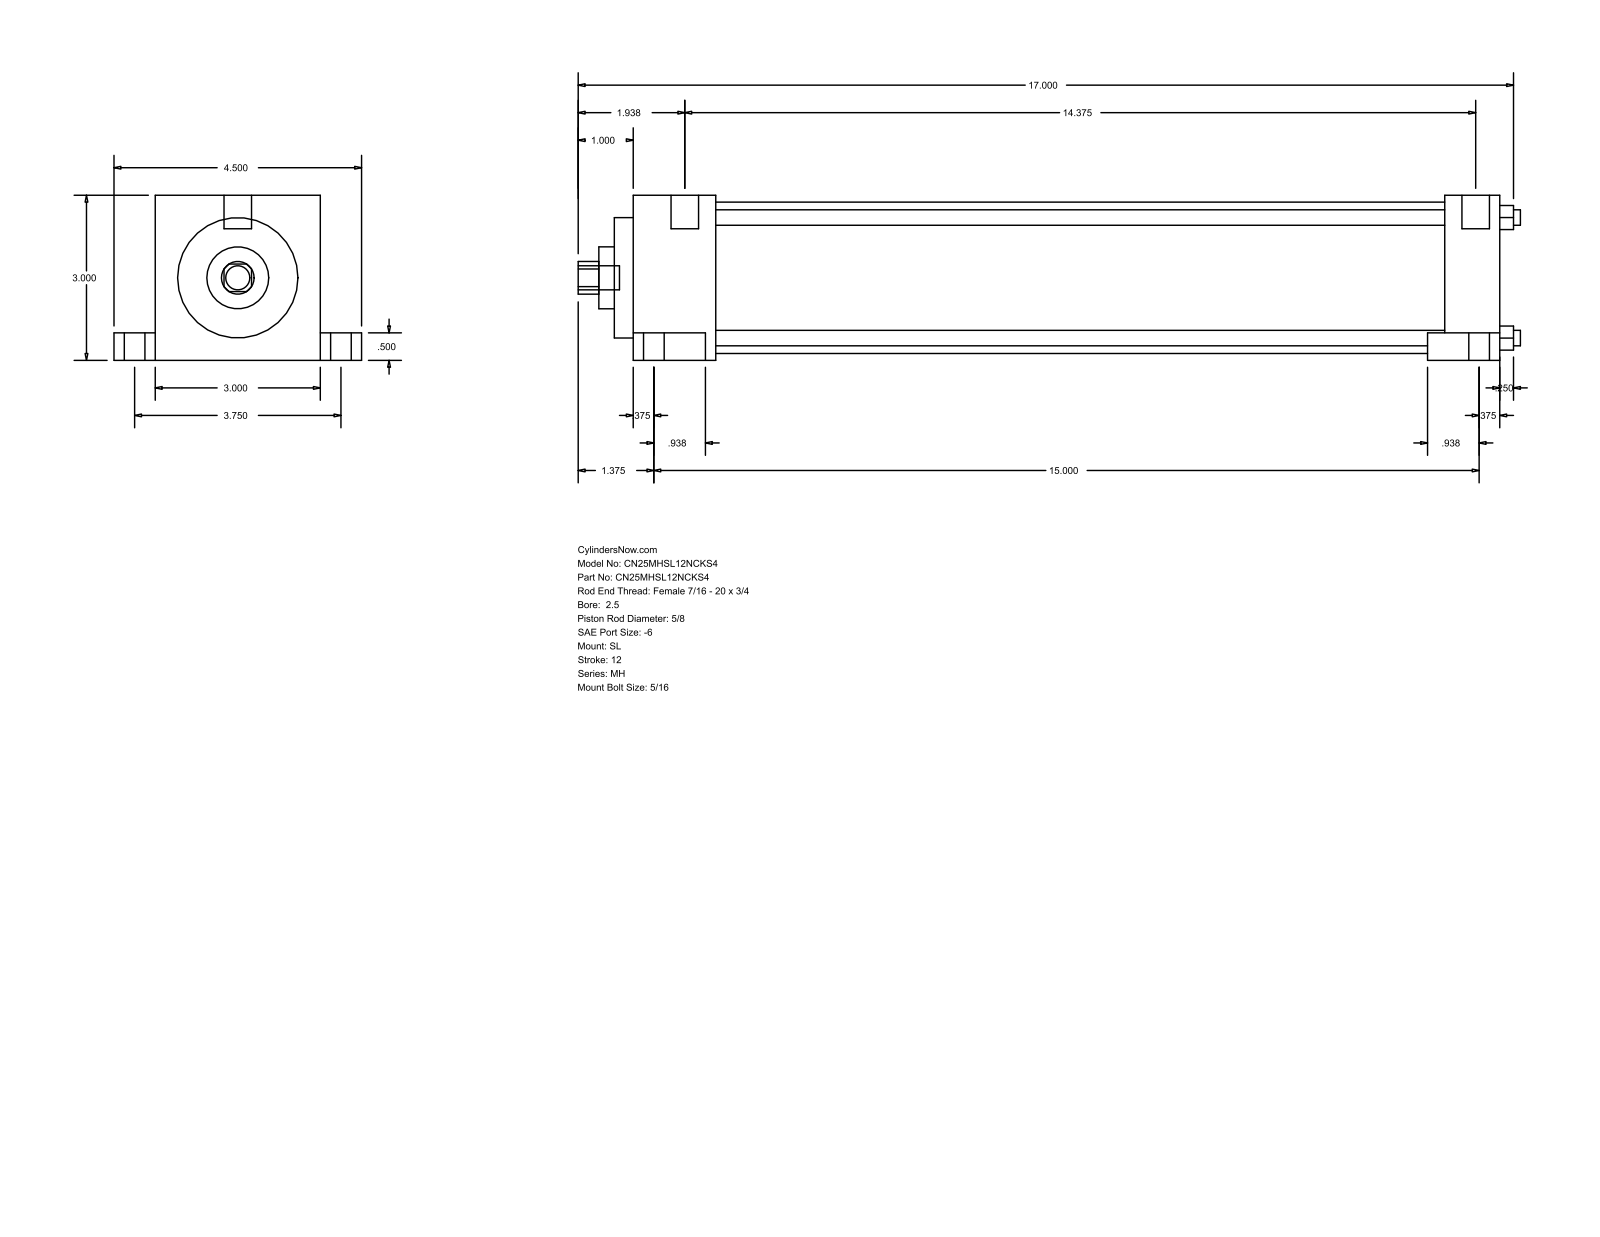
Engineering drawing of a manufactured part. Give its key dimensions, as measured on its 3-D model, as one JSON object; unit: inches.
{"part_name": "MH_SL__0250_0.625", "step_written_by": "GSSL Pune (CONFIG_CONTROL_DESIGN)", "units": "inches", "bodies": {"solids": 0, "faces": 86, "planar": 61, "cylindrical": 25, "other": 0}, "overall_size": [17.125, 4.5, 3], "round_holes": [[0.281, 4], [0.625, 1], [1.125, 1], [2.187, 1], [2.75, 1]], "round_bosses_or_shafts": [[0.625, 2], [0.375, 2], [0.219, 2], [0.5, 1], [0.437, 1]], "partial_cylinders_radius": [[0.297, 1]], "face_to_face_distances": [3, 1, 15.094, 16.094, 0.5, 2.5, 0.75, 3.75, 1.25, 14.781], "hole_center_spacings": [1.548, 2.19, 3.097]}
